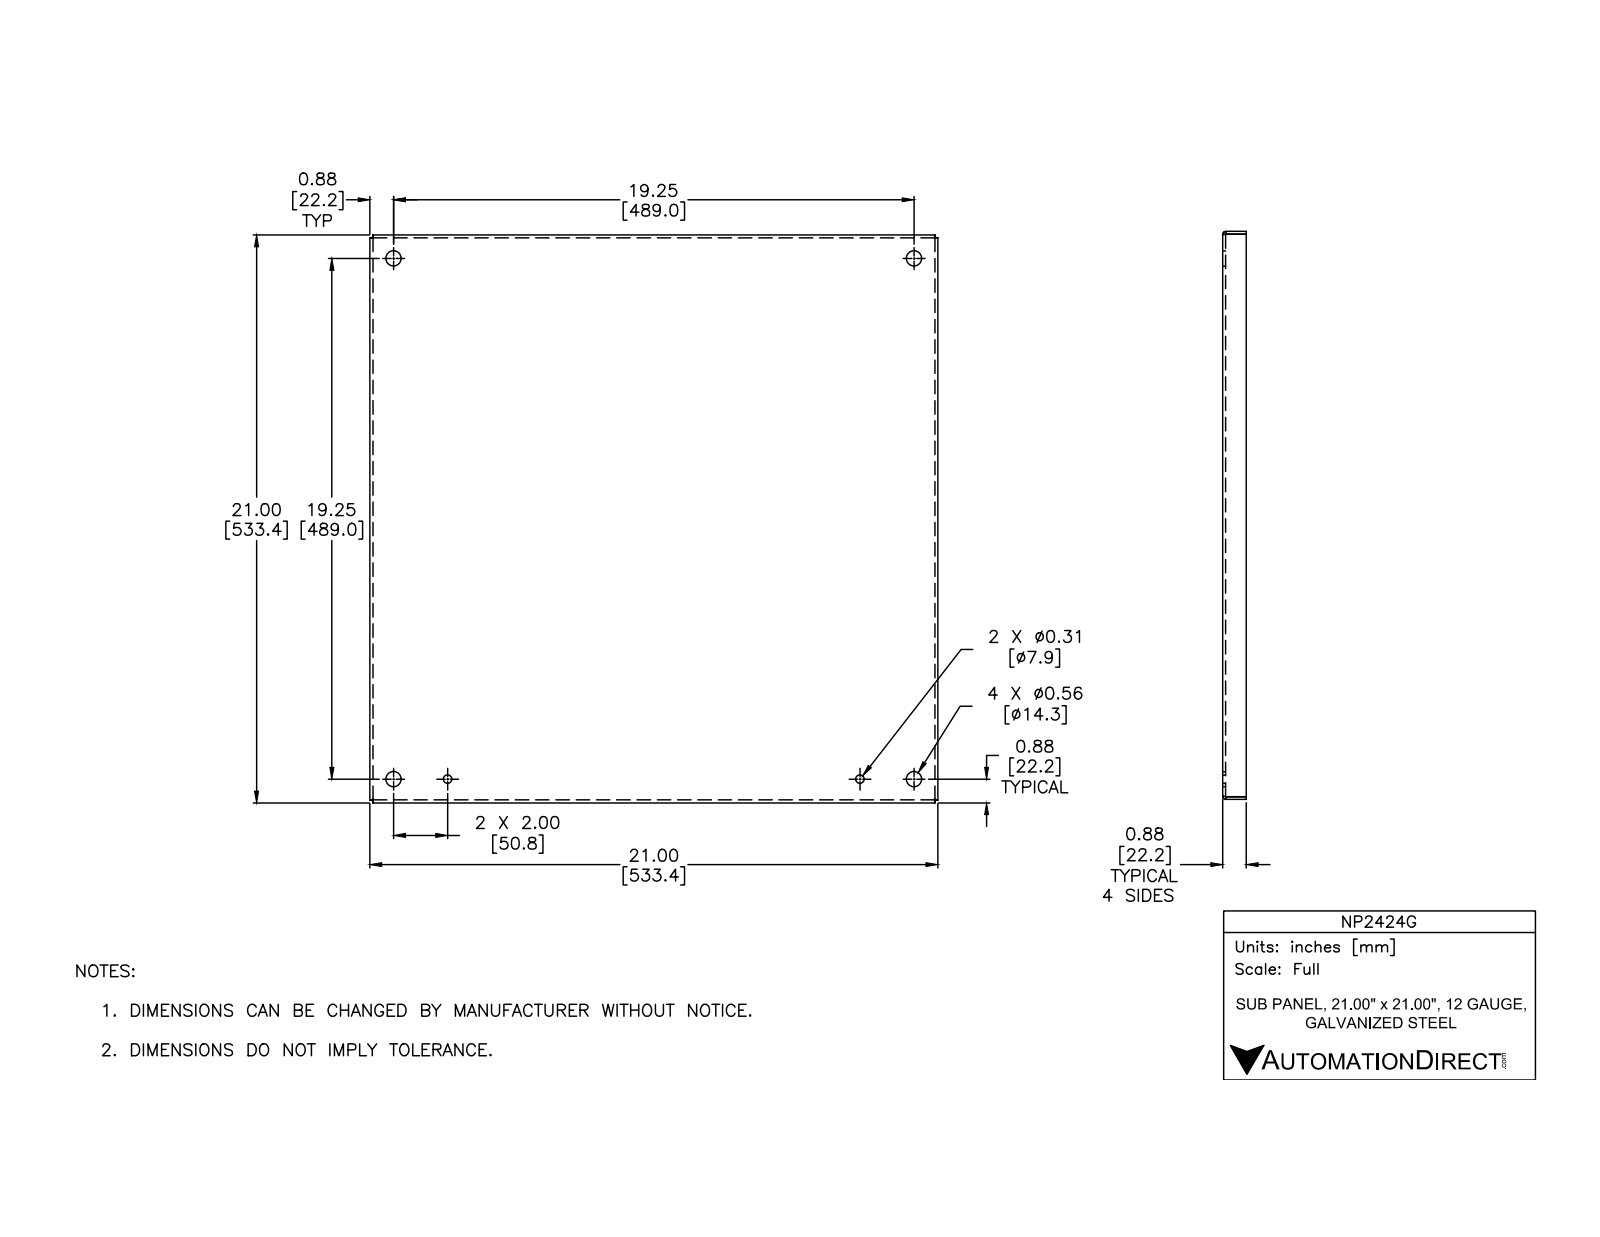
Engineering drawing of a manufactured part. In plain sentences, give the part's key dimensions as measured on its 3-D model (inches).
The part is named "NP2424G". Its 3-D file was written by "Autodesk Inventor 2012 (AUTOMOTIVE_DESIGN)". It is 1 solid with 44 faces: 22 planar, 14 cylindrical and 8 other. Overall it measures 21 by 21 by 0.875 inches. Its volume is 47.04 cubic inches and its surface area 1 013 square inches. Round holes: 4 of diameter 0.563, 2 of diameter 0.312. Partial cylindrical surfaces (rounded edges, fillets, slot ends): 4 of radius 0.031, 4 of radius 0.125. The main face-to-face distances are 0.094, 20.906, 21, 20.813, 0.781, 0.875, 0.105, 20.895, 20.802, 20.791. The hole center spacings are 19.25, 27.224, 2, 2, 15.25, 17.25, 17.25, 19.354.
